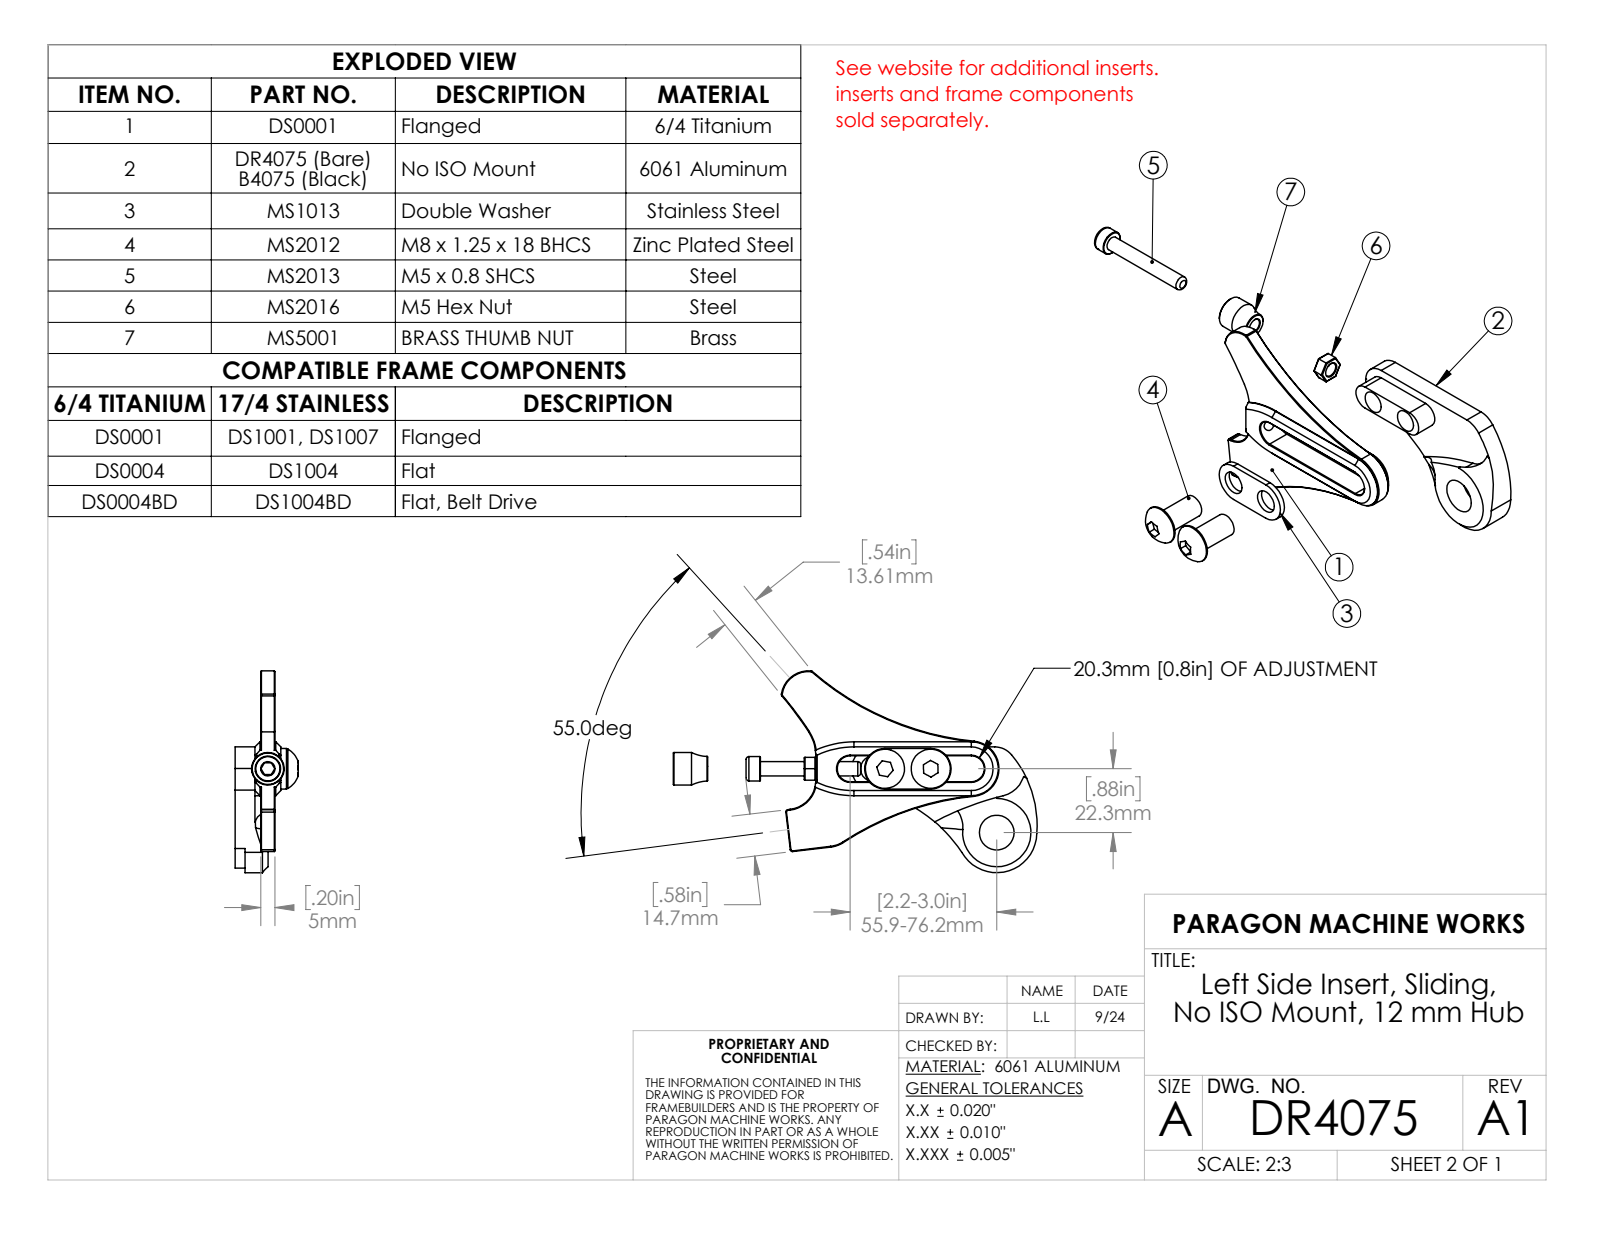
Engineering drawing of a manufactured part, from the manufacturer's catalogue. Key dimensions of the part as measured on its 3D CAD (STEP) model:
Part name (STEP PRODUCT): DR4075
STEP written by: SolidWorks 2023 (AUTOMOTIVE_DESIGN)
Units: inches
Bodies: 1 solid, 36 faces (12 planar, 20 cylindrical, 4 other)
Overall size (bounding box): 2.55 × 1.728 × 0.587
Volume: 0.82 in³ · Surface area: 9.937 in²
Round holes (diameter × count): ⌀0.312 ×2, ⌀0.477 ×1
Partial cylindrical surfaces — rounded edges, fillets, slot ends (radius × count): R0.178 ×2, R0.3 ×2, R0.3 ×1, R0.385 ×1, R0.394 ×1, R0.551 ×1, R0.787 ×1, R1.5 ×1
Main face-to-face distances: 0.274, 0.453, 0.179, 0.138, 0.136, 0.315, 0.356, 0.478, 0.122, 0.587
Hole centre spacings: 0.63, 1.262, 1.77
